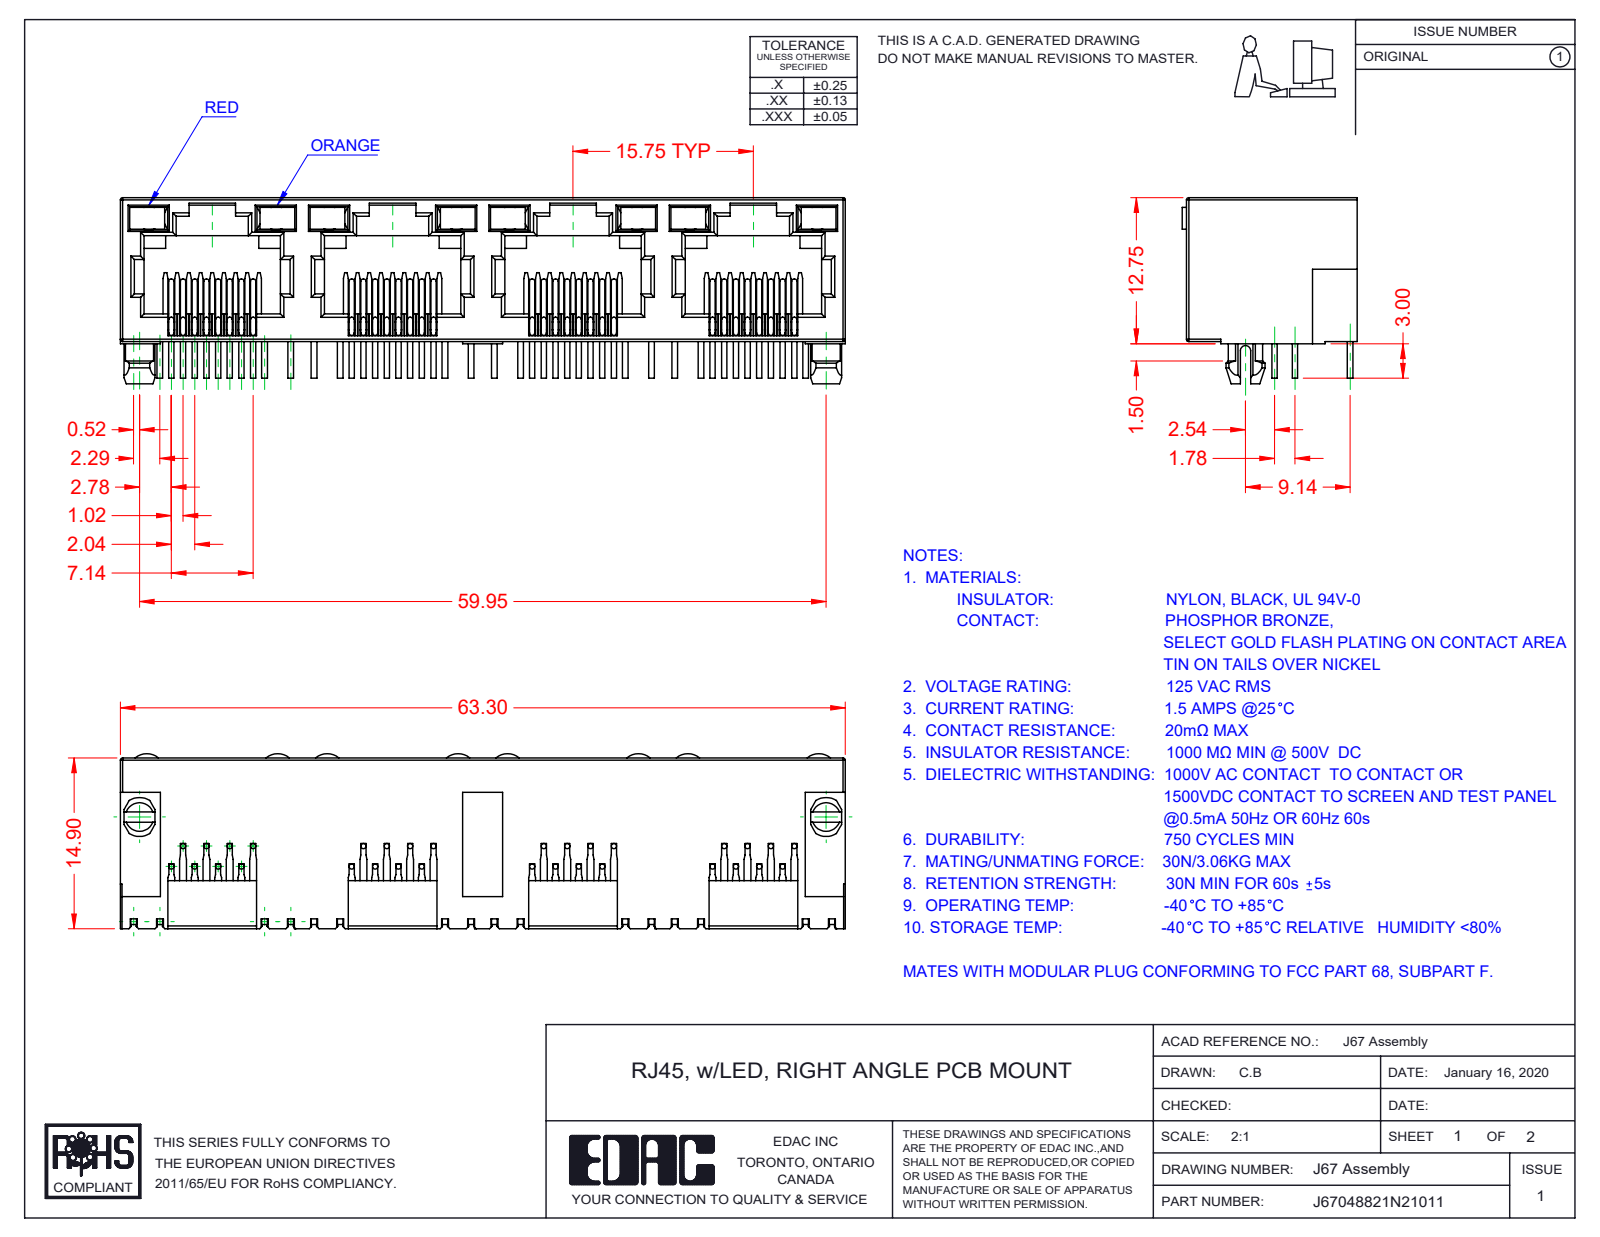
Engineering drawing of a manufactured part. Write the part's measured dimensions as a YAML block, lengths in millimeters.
part_name: "67 Insulator; J67048822N24011; 67 LED RH_4-Orange; 67 Contacts (+1 more)"
step_written_by: "SolidWorks 2016 (CONFIG_CONTROL_DESIGN)"
units: millimeters
bodies: {solids: 41, faces: 2465, planar: 1781, cylindrical: 476, other: 208}
overall_size: [63.3, 16.25, 15.28]
volume: 5159
surface_area: 11573
round_bosses_or_shafts:
  - {diameter: 0.46, count: 96}
partial_cylinders:
  - {radius: 0.2, count: 66}
  - {radius: 0.3, count: 29}
  - {radius: 0.45, count: 9}
  - {radius: 1.55, count: 8}
  - {radius: 1.5, count: 2}
  - {radius: 1.7, count: 2}
  - {radius: 0.35, count: 1}
  - {radius: 1, count: 1}
face_to_face_distances: [0.5, 12.55, 1.89, 0.89, 10, 15.75, 1, 1.39, 11, 11.89]
